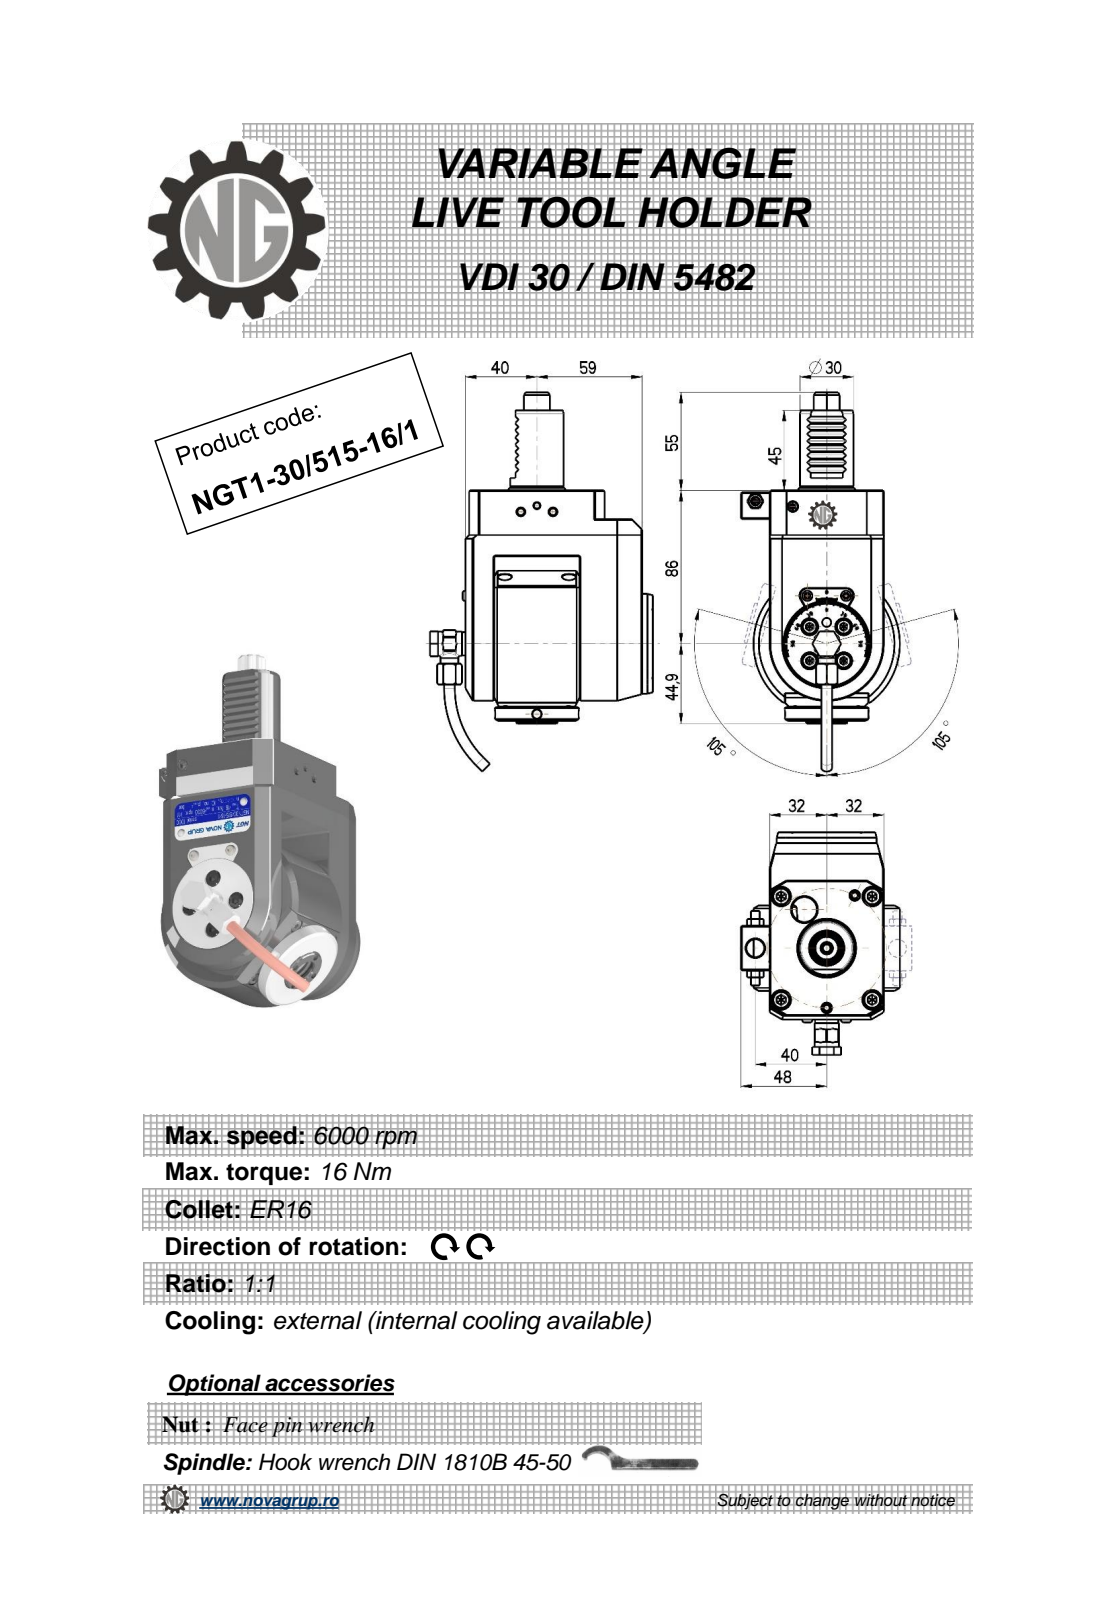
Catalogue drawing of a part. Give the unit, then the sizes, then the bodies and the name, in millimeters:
Units: millimetres
Overall size (bounding box): 212.67 × 124.9 × 89
Round holes (diameter × count): ⌀3.2 ×4, ⌀4 ×3, ⌀4.2 ×2, ⌀5 ×2, ⌀10 ×2, ⌀3 ×1, ⌀5.3 ×1, ⌀6.2 ×1, ⌀9 ×1, ⌀9.5 ×1, ⌀11 ×1, ⌀12.5 ×1
Round bosses / shafts (diameter × count): ⌀6 ×2, ⌀5.7 ×2, ⌀82 ×1, ⌀56 ×1, ⌀47 ×1, ⌀35 ×1, ⌀30 ×1, ⌀23 ×1
Partial cylindrical surfaces — rounded edges, fillets, slot ends (radius × count): R2.91 ×16, R0.26 ×12, R0.3 ×8, R0.16 ×6, R0.5 ×4, R1 ×2, R5.75 ×1, R7.25 ×1
Main face-to-face distances: 64, 16, 37, 99, 6, 105, 21, 14, 35, 48
Hole centre spacings: 9.25, 13.08, 18.5, 41.06, 49.87, 50.26, 0.4, 30.75
Volume: 753 024 mm³ · Surface area: 70 640 mm²
Bodies: 1 solid, 520 faces (193 planar, 164 cylindrical, 163 other)
Part name (STEP PRODUCT): NGT1_30_515_16_1
STEP written by: PRO/ENGINEER BY PARAMETRIC TECHNOLOGY CORPORATION, 2010280 (CONFIG_CONTROL_DESIGN)
